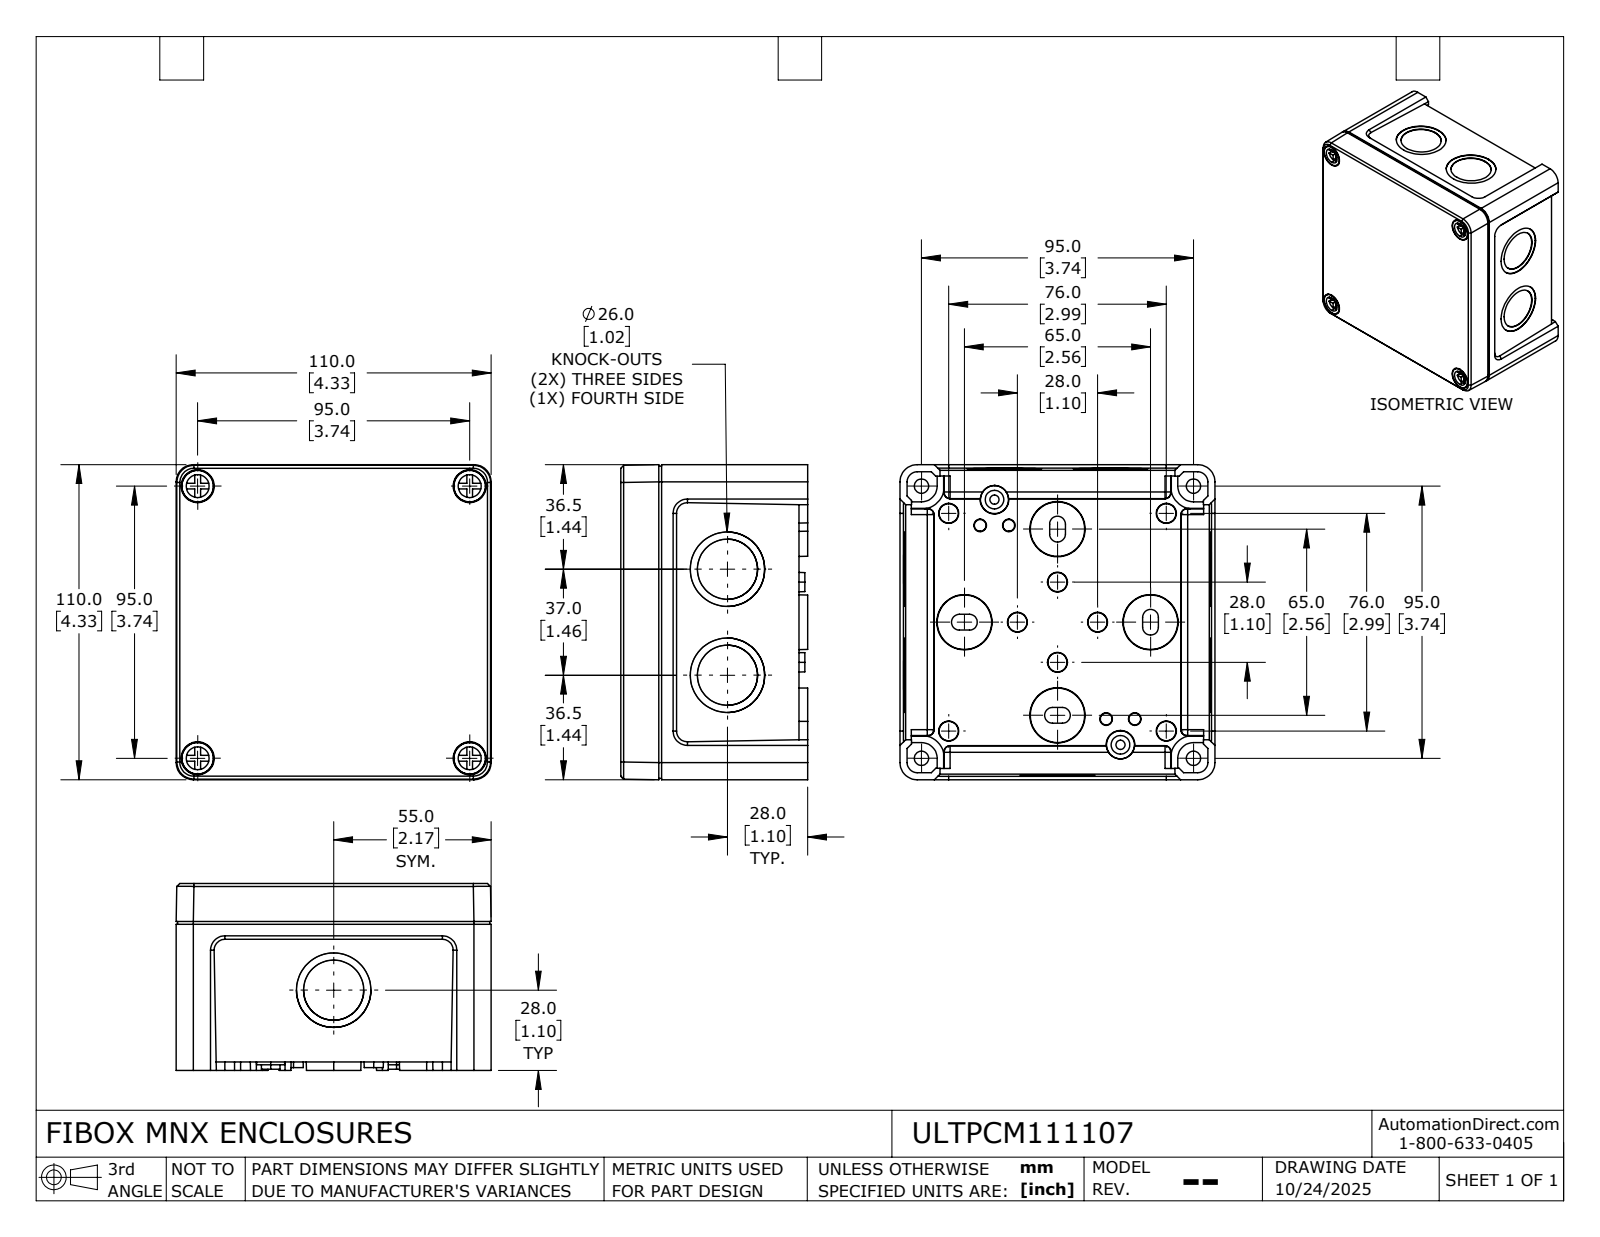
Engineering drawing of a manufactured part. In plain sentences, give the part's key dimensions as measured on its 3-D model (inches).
The part is named "ULTPCM111107_Default". Its 3-D file was written by "SolidWorks 2024 (CONFIG_CONTROL_DESIGN)". It is 6 solids with 685 faces: 354 planar, 206 cylindrical and 125 other. Overall it measures 4.331 by 4.331 by 2.569 inches. Its volume is 9.263 cubic inches and its surface area 187.5 square inches. Round holes: 10 of diameter 0.126, 9 of diameter 0.827, 7 of diameter 1.024, 4 of diameter 0.197, 4 of diameter 0.315. Round bosses or shafts: 4 of diameter 0.433, 4 of diameter 0.283, 2 of diameter 0.256. Partial cylindrical surfaces (rounded edges, fillets, slot ends): 24 of radius 0.079, 8 of radius 0.02, 8 of radius 0.039, 8 of radius 0.104, 8 of radius 0.108, 8 of radius 0.236, 4 of radius 0.091, 4 of radius 0.197. The main face-to-face distances are 0.074, 0.108, 0.079, 2.175, 0.197, 2.067, 2.254, 2.146, 4.287, 4.213. The hole center spacings are 1.769, 2.288, 2.535, 3.059, 3.387, 0.529, 0.78, 1.075.
